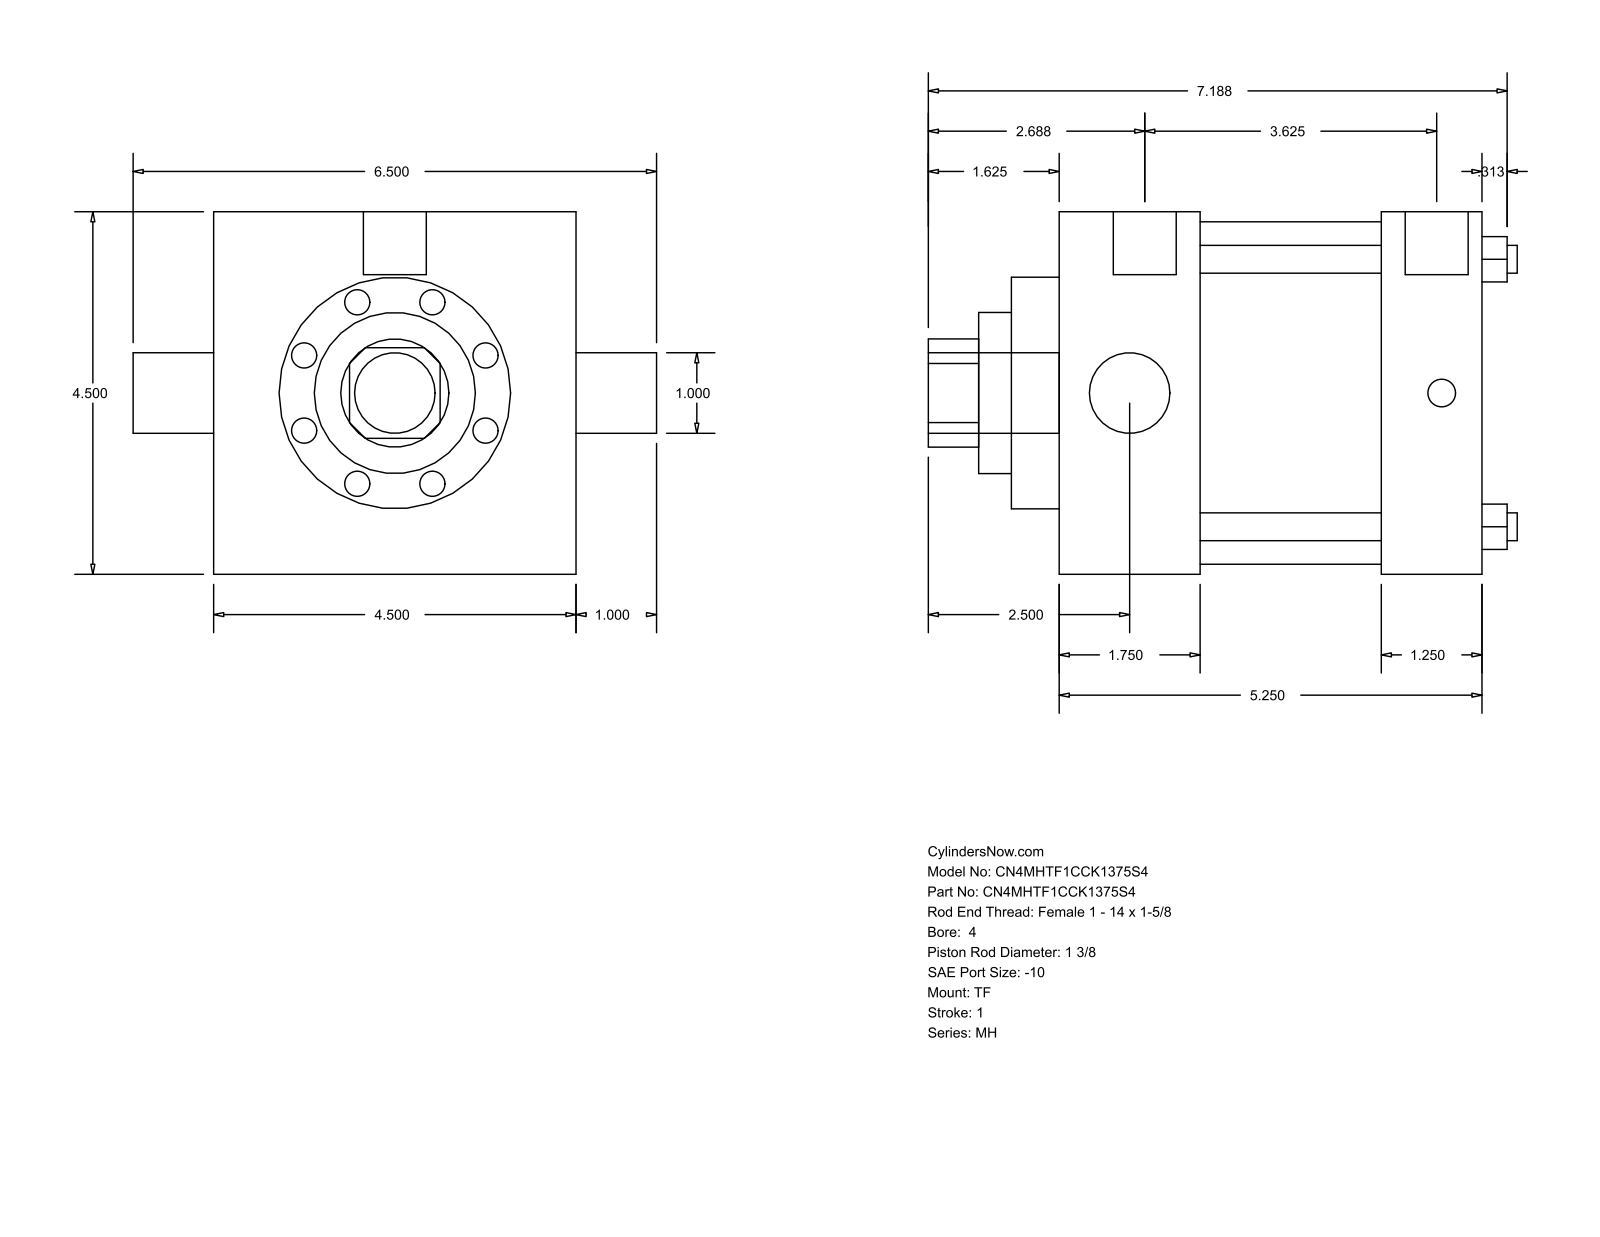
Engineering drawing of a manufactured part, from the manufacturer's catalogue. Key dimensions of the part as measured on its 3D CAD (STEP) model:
Part name (STEP PRODUCT): MH_TF__0400_1.375
STEP written by: GSSL Pune (CONFIG_CONTROL_DESIGN)
Units: millimetres
Bodies: 0 solids, 86 faces (61 planar, 25 cylindrical, 0 other)
Overall size (bounding box): 185.74 × 165.1 × 114.3
Round holes (diameter × count): ⌀8.76 ×4, ⌀25.4 ×1, ⌀34.92 ×1, ⌀50.8 ×1, ⌀73.03 ×1, ⌀107.95 ×1
Round bosses / shafts (diameter × count): ⌀8.73 ×3, ⌀19.84 ×2, ⌀25.4 ×1
Partial cylindrical surfaces — rounded edges, fillets, slot ends (radius × count): R17.06 ×1
Main face-to-face distances: 114.3, 133.35, 44.45, 88.9, 101.61, 57.16, 31.74, 15.08, 59.53, 116.69
Hole centre spacings: 59.62, 84.32, 119.25
